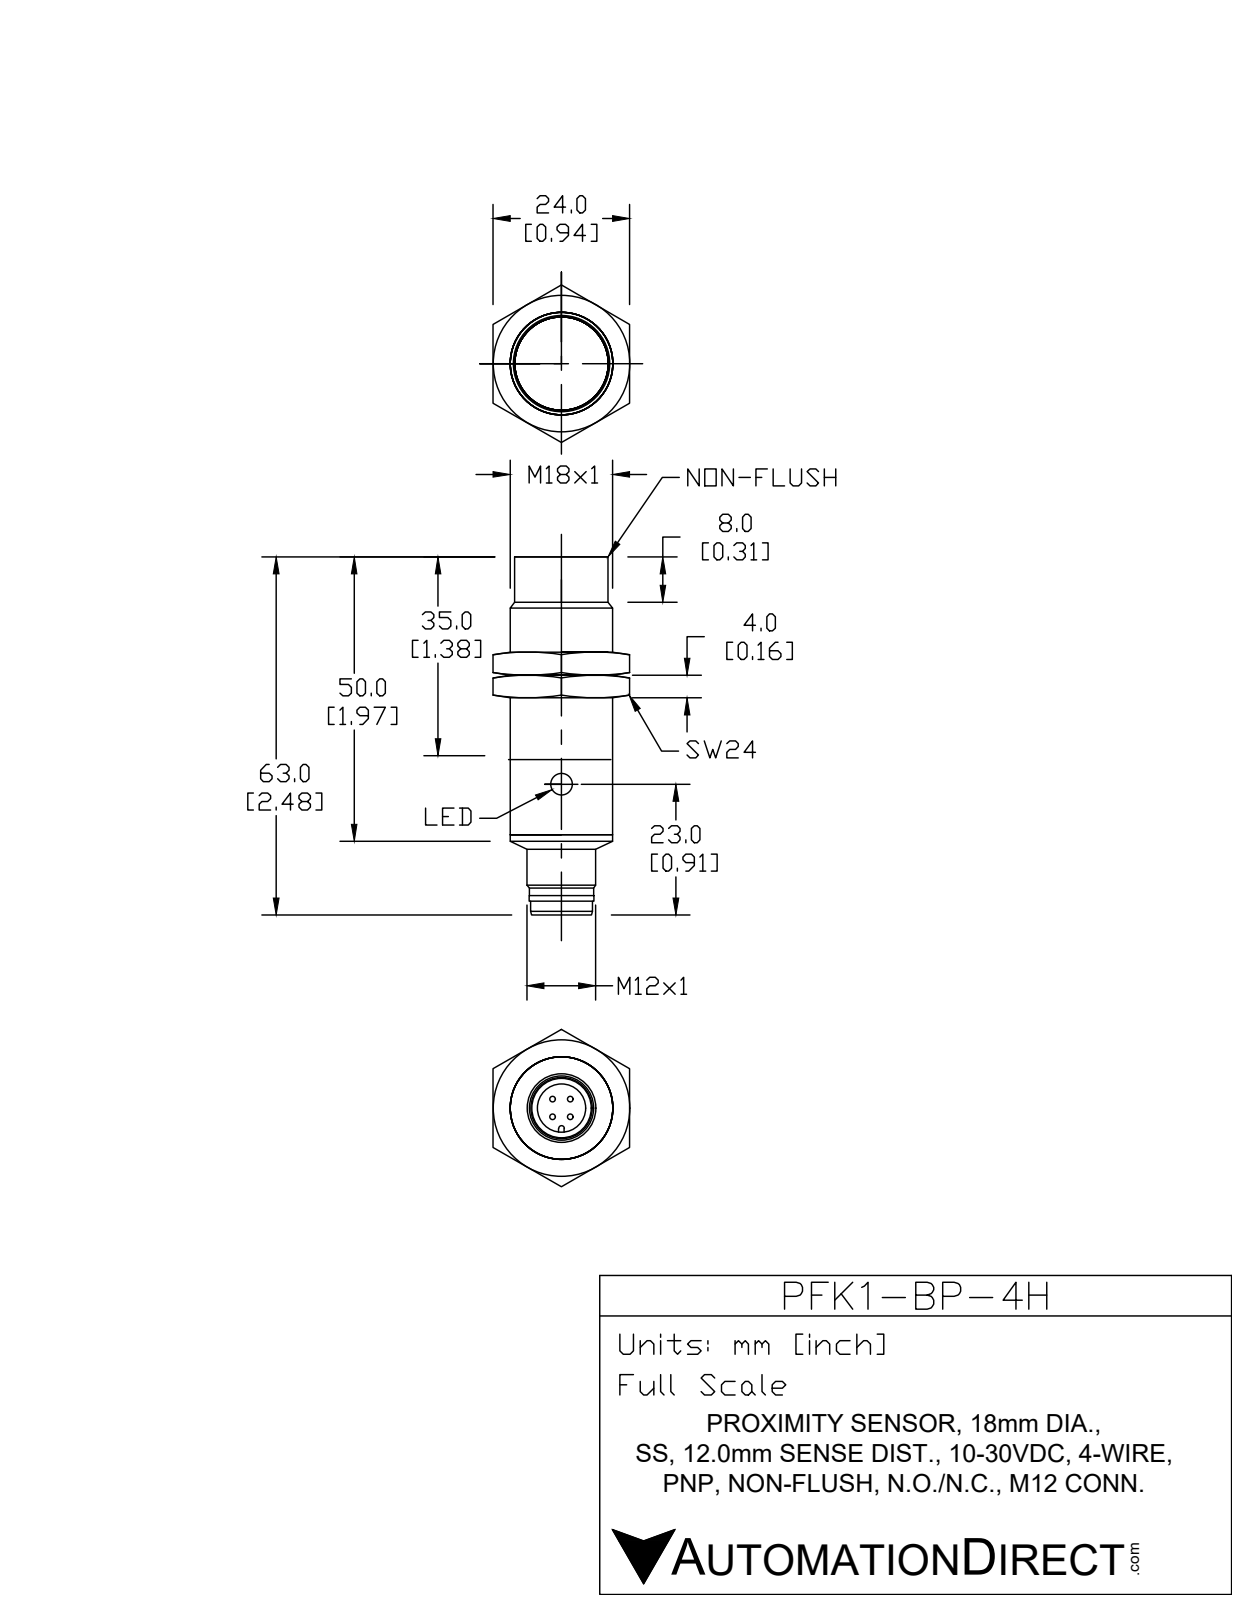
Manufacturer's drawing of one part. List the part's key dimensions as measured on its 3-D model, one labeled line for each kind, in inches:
Part name (STEP PRODUCT): PFK1-BP-4H
STEP written by: SolidWorks 2017 (AUTOMOTIVE_DESIGN)
Units: inches
Bodies: 4 solids, 69 faces (12 planar, 35 cylindrical, 22 other)
Overall size (bounding box): 2.484 × 0.709 × 0.709
Volume: 0.811 in³ · Surface area: 8.999 in²
Round holes (diameter × count): ⌀0.157 ×1, ⌀0.331 ×1, ⌀0.335 ×1, ⌀0.374 ×1, ⌀0.622 ×1
Round bosses / shafts (diameter × count): ⌀0.039 ×4, ⌀0.709 ×1, ⌀0.472 ×1, ⌀0.413 ×1, ⌀0.37 ×1
Partial cylindrical surfaces — rounded edges, fillets, slot ends (radius × count): R0.024 ×1, R0.326 ×1
Main face-to-face distances: 1.539, 0.394, 1.933, 2.087, 1.693, 0.154, 2.134, 1.74, 0.201, 0.047
